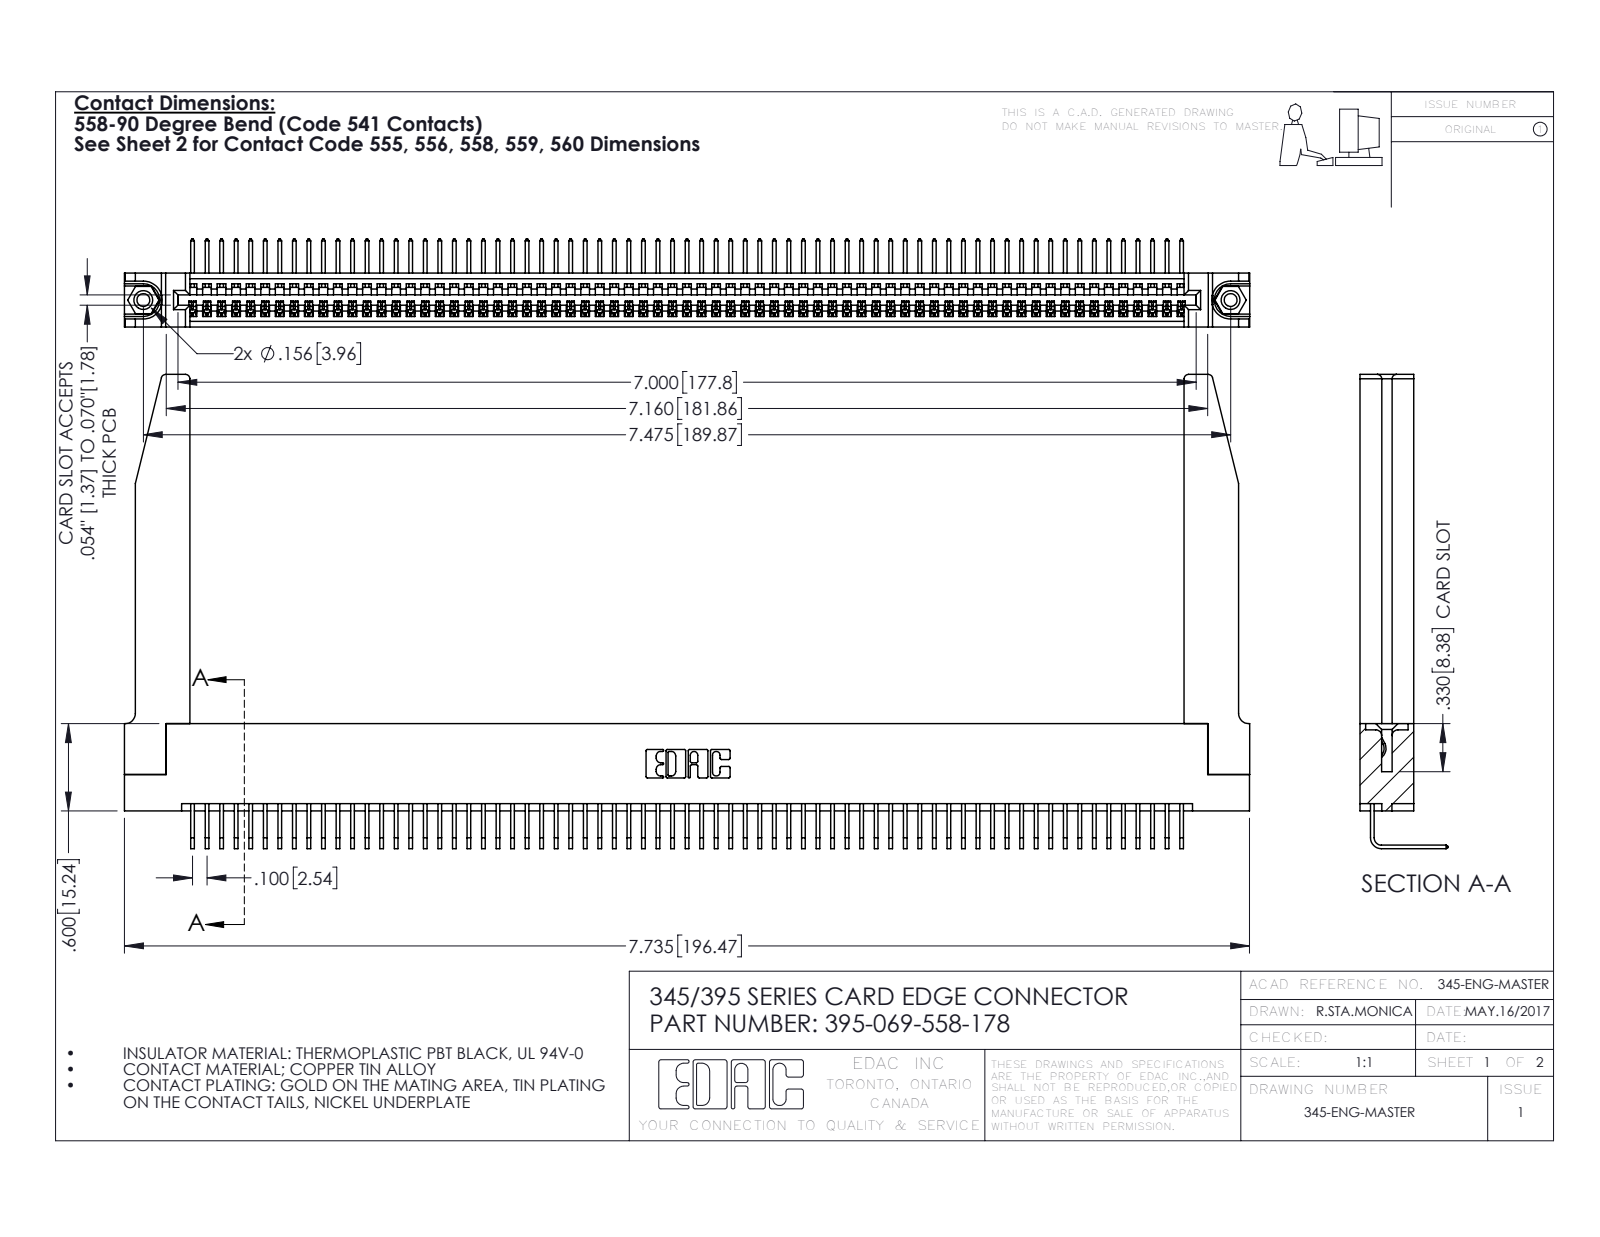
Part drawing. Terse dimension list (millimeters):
name: 345-292-001_558 Tail - 2; 345-220-078_345-220-078; 395-069-558-178; 345-250-001_345-250-001-102 (+1 more)
written by: SolidWorks 2016 (CONFIG_CONTROL_DESIGN)
unit: mm
bodies: 74 solids, 4500 faces (3120 planar, 1328 cylindrical, 52 other)
size: 196.5 × 82.8 × 15.4
volume: 26 890 mm³; area: 33 970 mm²
holes: 2× ⌀2.3, 2× ⌀3.2, 2× ⌀4, 1× ⌀1.6
bosses: 2× ⌀3.9
rounds: 138× R0.2, 22× R0.3, 8× R0.8, 6× R0.2, 6× R0.8, 3× R0.7, 2× R0.8, 2× R1
face distances: 1.8, 9.4, 7.6, 5.1, 2.5, 6.9, 0.6, 5.7, 3.8, 3.8
hole spacings: 6.9, 183.9, 189.9
